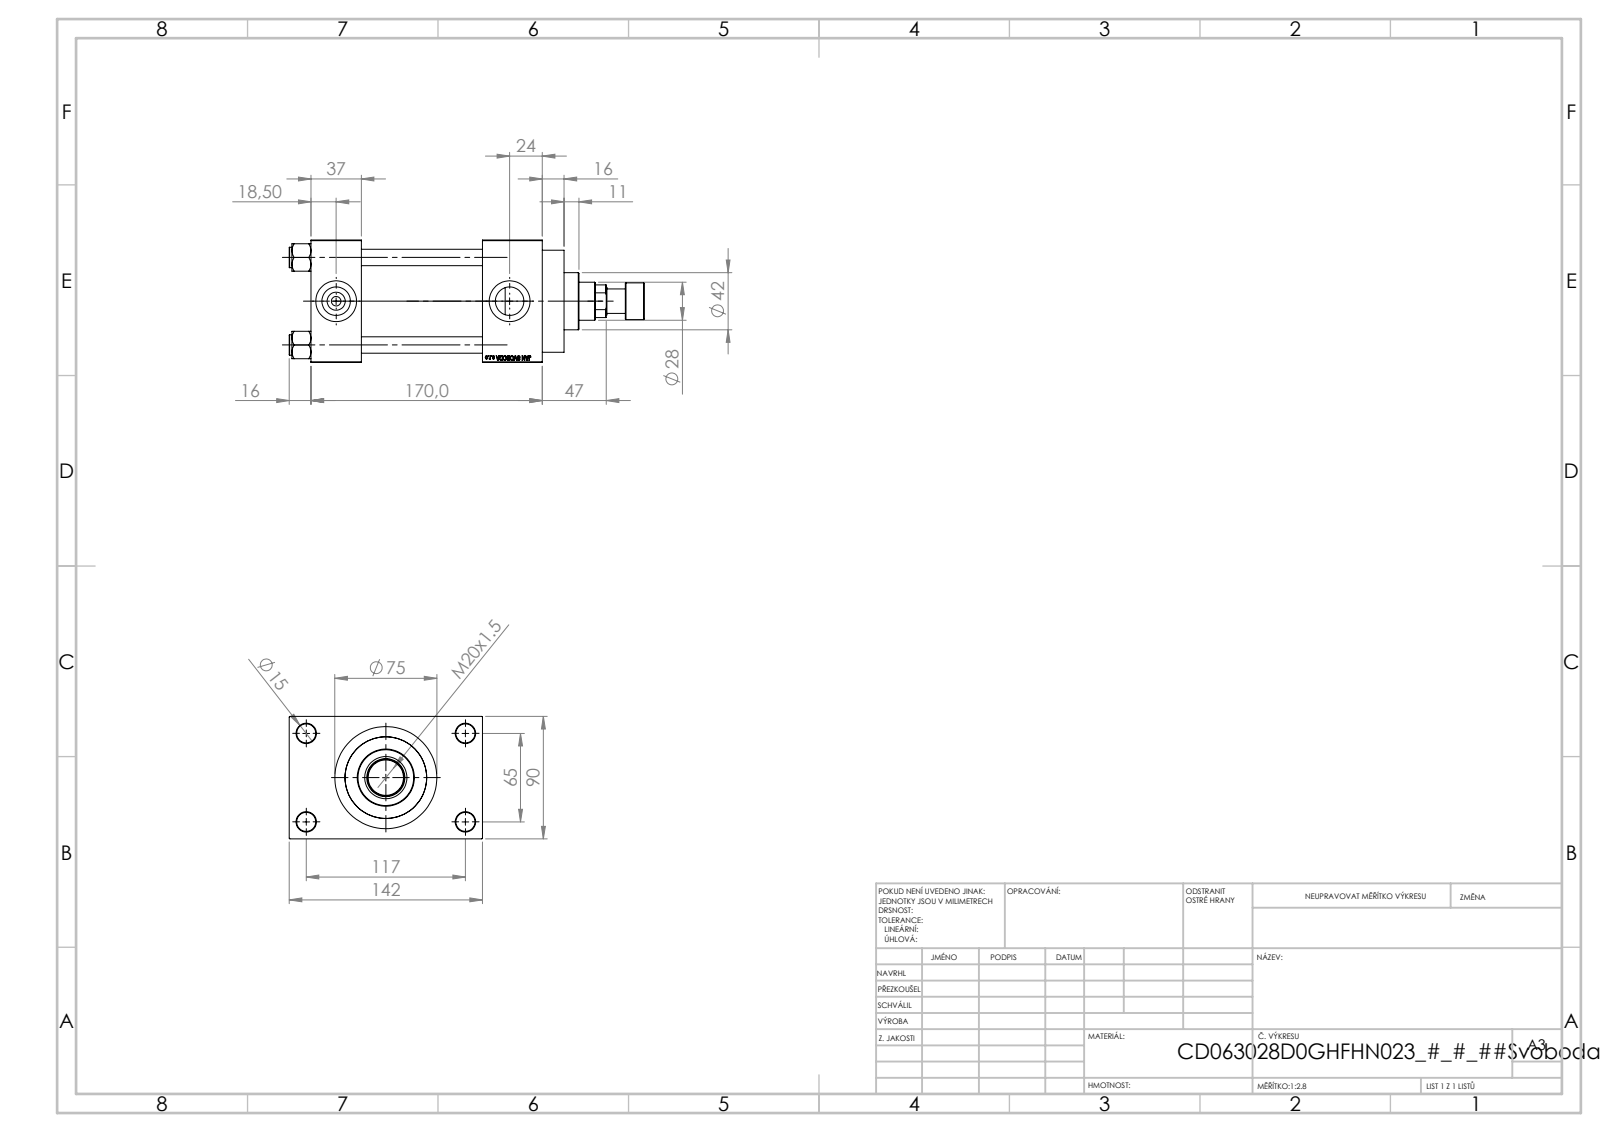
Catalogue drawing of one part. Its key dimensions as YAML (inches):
part_name: "V215CD_NUT_M5_D; V215CD_D_Body; V215CD_VC_A; V215CR_ROD_END_F (+2 more)"
step_written_by: "SolidWorks 2019 (CONFIG_CONTROL_DESIGN)"
units: inches
bodies: {solids: 12, faces: 1117, planar: 501, cylindrical: 92, other: 524}
overall_size: [10.276, 5.591, 3.543]
volume: 70.73
surface_area: 345.9
round_holes:
  - {diameter: 0.472, count: 4}
  - {diameter: 0.551, count: 4}
  - {diameter: 0.276, count: 2}
  - {diameter: 0.825, count: 2}
  - {diameter: 1.181, count: 2}
  - {diameter: 0.728, count: 1}
  - {diameter: 1.102, count: 1}
  - {diameter: 1.22, count: 1}
  - {diameter: 1.969, count: 1}
  - {diameter: 2.362, count: 1}
  - {diameter: 2.48, count: 1}
round_bosses_or_shafts:
  - {diameter: 0.591, count: 4}
  - {diameter: 2.953, count: 1}
  - {diameter: 2.717, count: 1}
  - {diameter: 1.654, count: 1}
  - {diameter: 1.063, count: 1}
  - {diameter: 0.709, count: 1}
face_to_face_distances: [3.543, 3.504, 1.457, 4.961, 5.236, 6.693, 1.732, 1.024, 4.567, 5.591]
hole_center_spacings: [1.037, 1.79, 2.531, 2.635, 2.748, 3.569, 4.383, 2.559]
